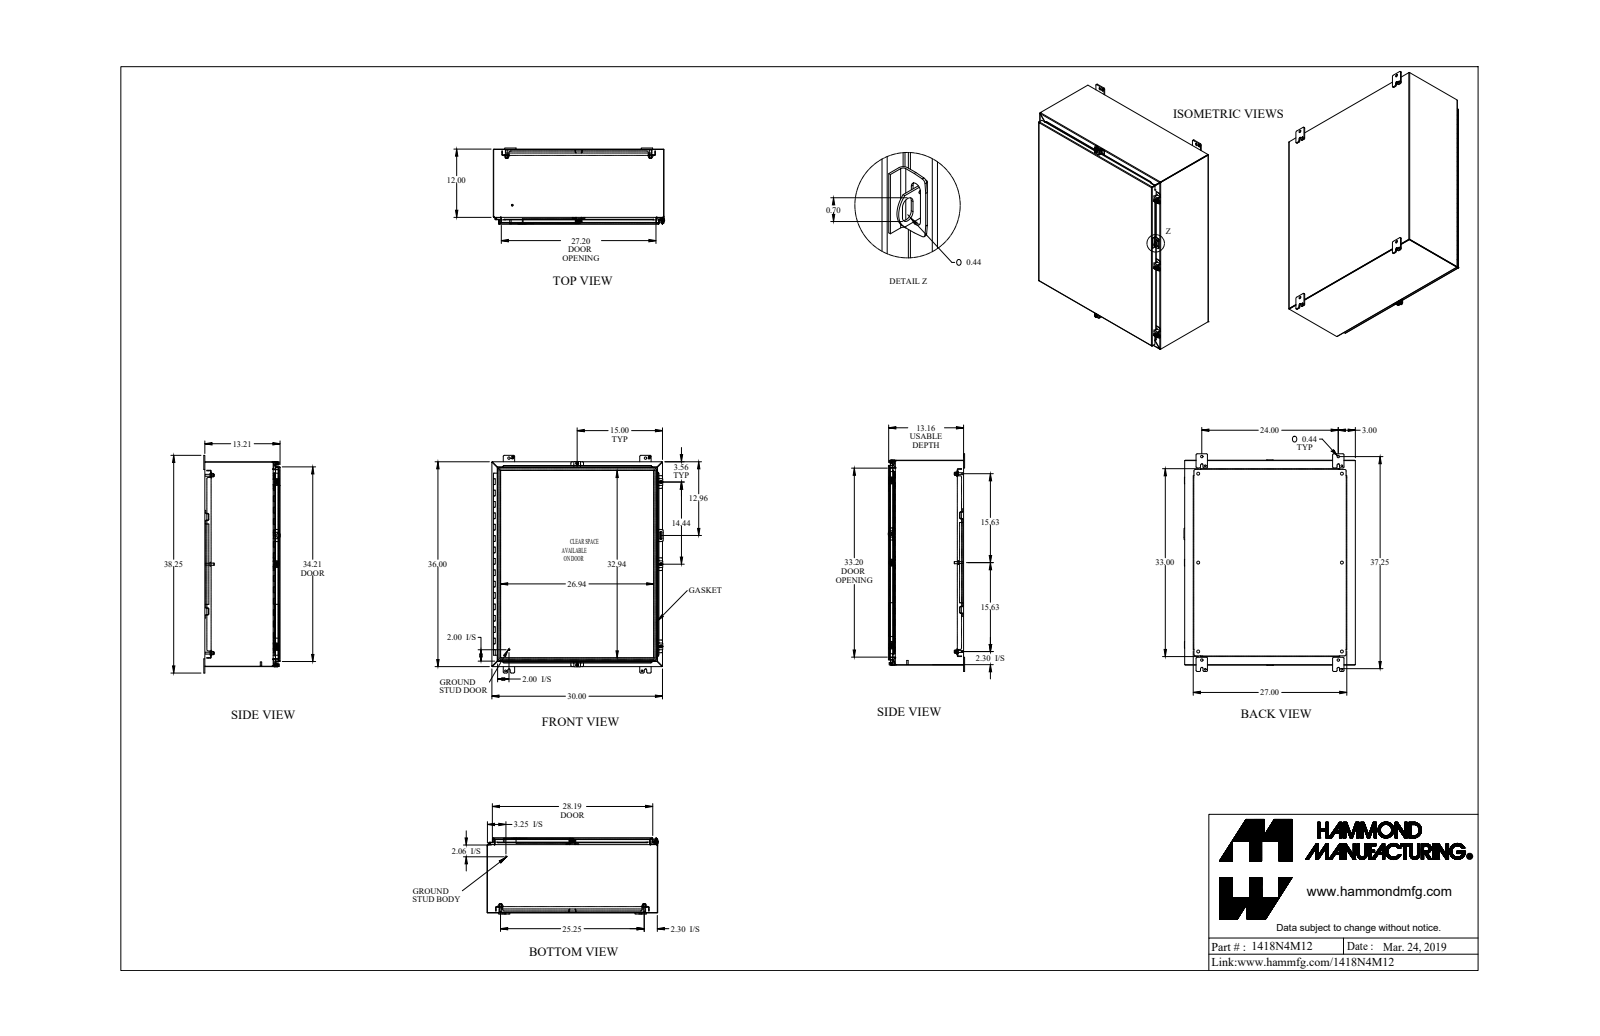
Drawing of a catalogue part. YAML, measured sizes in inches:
part_name: "1418N4M12_Default"
step_written_by: "SolidWorks 2019 (CONFIG_CONTROL_DESIGN)"
units: inches
bodies: {solids: 54, faces: 1823, planar: 1063, cylindrical: 650, other: 110}
overall_size: [38.25, 30.126, 13.437]
volume: 419.5
surface_area: 11015
round_holes:
  - {diameter: 0.5, count: 6}
  - {diameter: 0.213, count: 5}
  - {diameter: 0.265, count: 5}
  - {diameter: 0.307, count: 4}
  - {diameter: 0.313, count: 4}
  - {diameter: 0.375, count: 4}
  - {diameter: 0.437, count: 4}
  - {diameter: 0.445, count: 2}
  - {diameter: 0.445, count: 2}
  - {diameter: 0.125, count: 1}
  - {diameter: 0.187, count: 1}
  - {diameter: 0.375, count: 1}
round_bosses_or_shafts:
  - {diameter: 0.65, count: 6}
  - {diameter: 0.375, count: 6}
  - {diameter: 0.33, count: 6}
  - {diameter: 0.5, count: 5}
  - {diameter: 0.39, count: 5}
  - {diameter: 0.244, count: 5}
  - {diameter: 1, count: 4}
  - {diameter: 0.281, count: 2}
partial_cylinders:
  - {radius: 0.188, count: 38}
  - {radius: 0.25, count: 36}
  - {radius: 0.048, count: 27}
  - {radius: 0.143, count: 27}
  - {radius: 0.036, count: 22}
  - {radius: 0.108, count: 22}
  - {radius: 0.116, count: 12}
  - {radius: 0.125, count: 12}
face_to_face_distances: [0.072, 0.072, 13.066, 13.138, 13.138, 13.21, 12.106, 12.034, 1.032, 1.104]
hole_center_spacings: [40.176, 15.625, 25.25, 12.802, 12.803, 21.782, 24, 31.25]
